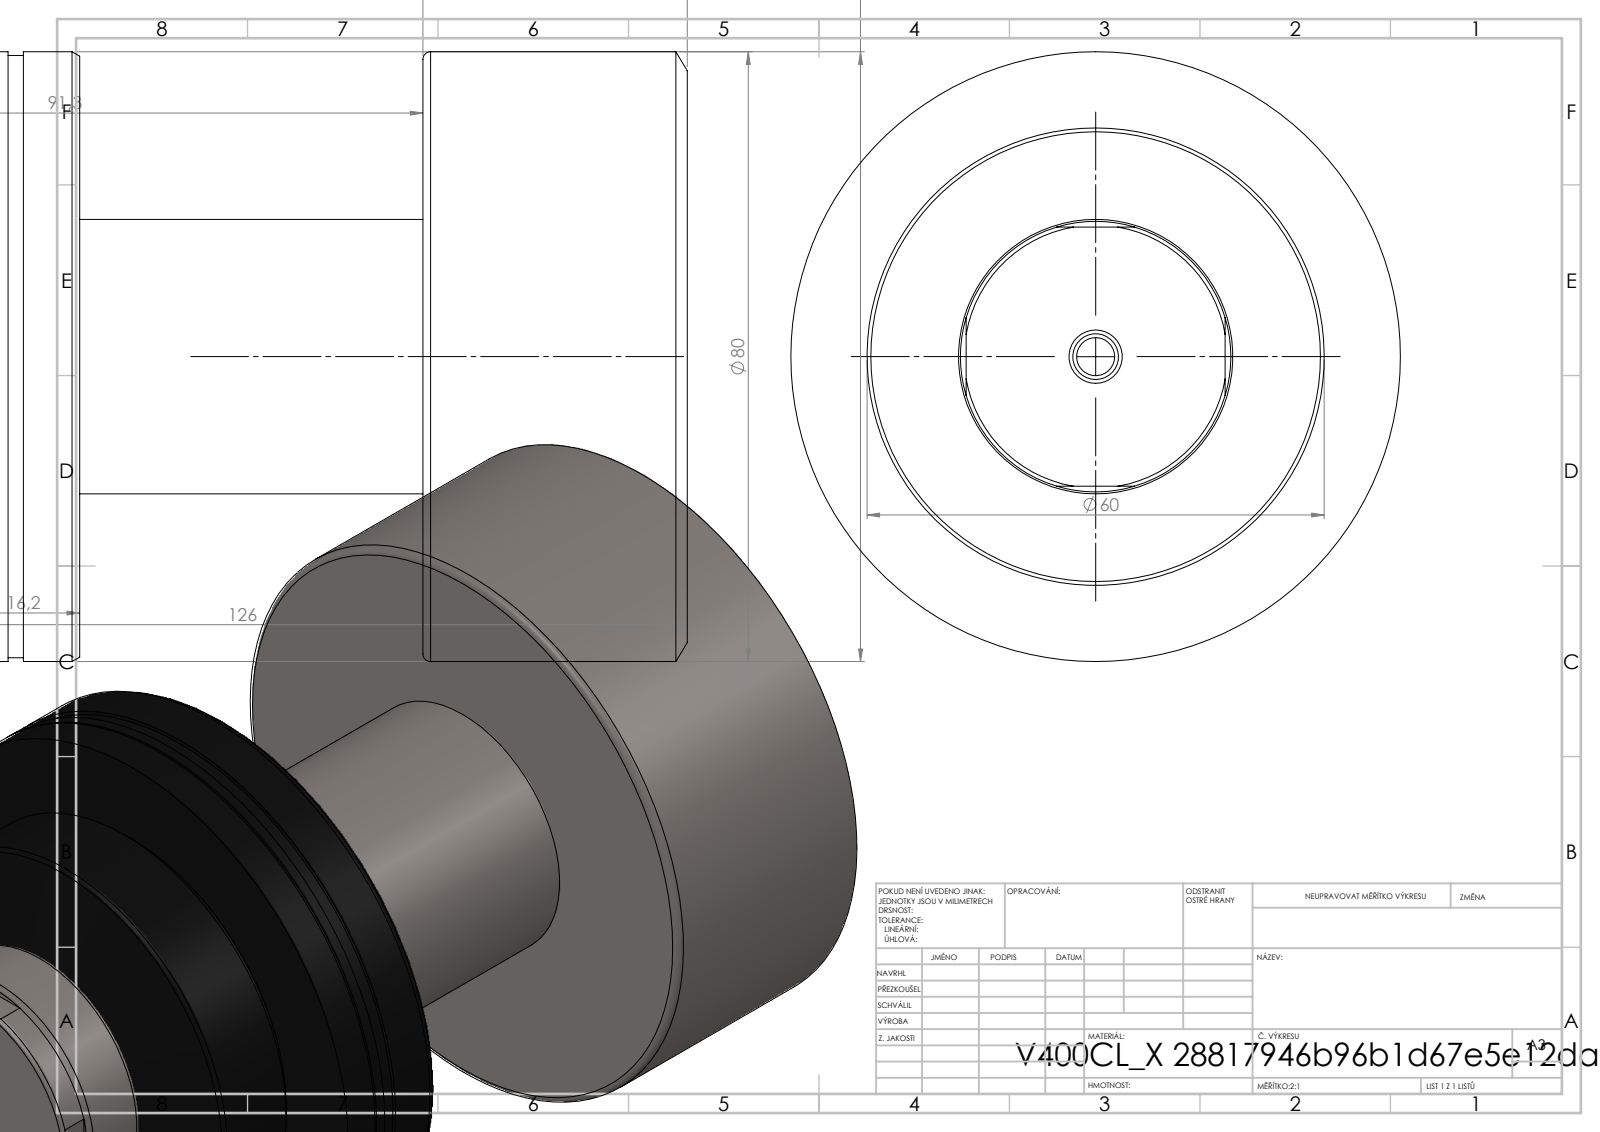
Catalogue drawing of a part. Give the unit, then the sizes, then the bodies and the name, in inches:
Units: inches
Overall size (bounding box): 4.961 × 3.15 × 3.15
Round holes (diameter × count): ⌀0.081 ×1, ⌀0.197 ×1, ⌀0.236 ×1, ⌀1.417 ×1
Round bosses / shafts (diameter × count): ⌀3.15 ×1, ⌀3.11 ×1, ⌀2.362 ×1
Partial cylindrical surfaces — rounded edges, fillets, slot ends (radius × count): R0.699 ×1
Main face-to-face distances: 1.366, 3.14, 1.774, 3.778, 2.411, 0.638, 4.961, 3.594, 1.821, 1.183
Volume: 21.79 in³ · Surface area: 74.6 in²
Bodies: 2 solids, 74 faces (18 planar, 28 cylindrical, 28 other)
Part name (STEP PRODUCT): V400CL_PC_X; V400CL_VC_X
STEP written by: SolidWorks 2019 (CONFIG_CONTROL_DESIGN)
